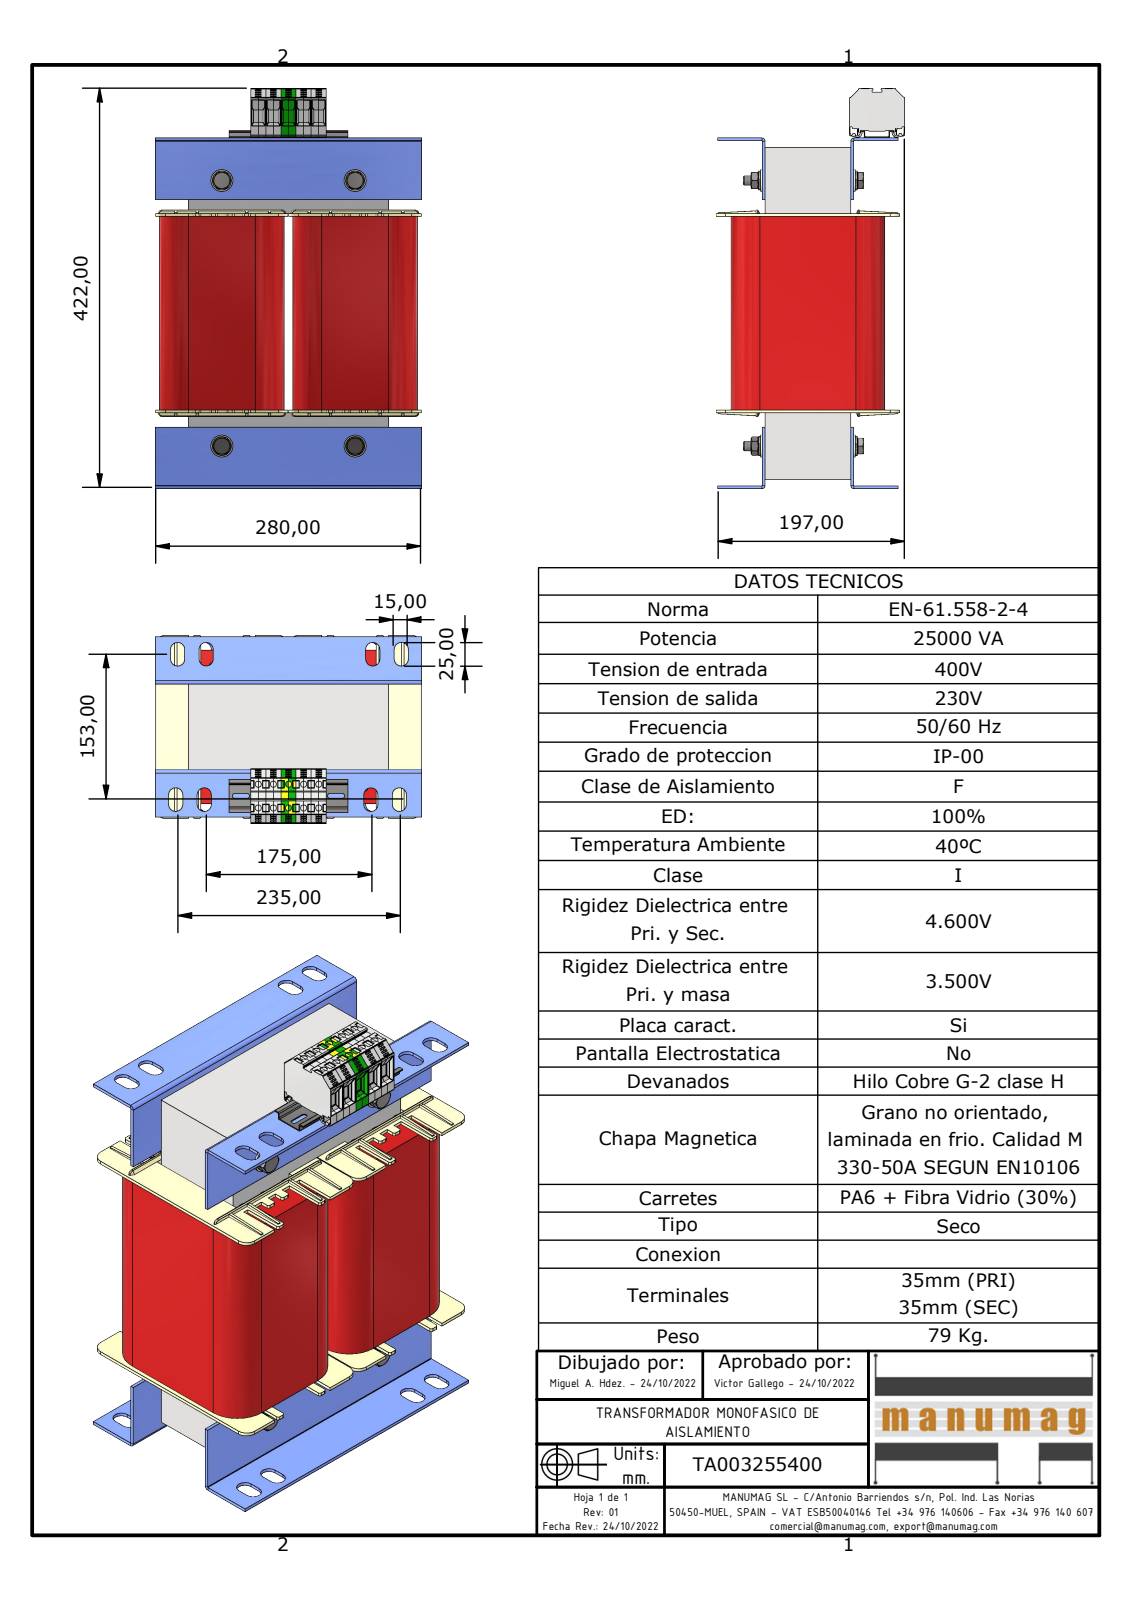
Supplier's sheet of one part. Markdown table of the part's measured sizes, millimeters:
| quantity | value |
| --- | --- |
| part name | TA003255400; UI350 x 210 - 90 (Rc70); RC 70 UI; centrador M10 (+7 more) |
| STEP written by | Autodesk Inventor 2023 (AUTOMOTIVE_DESIGN) |
| units | millimeters |
| bodies | 37 solids, 4798 faces (2768 planar, 1386 cylindrical, 644 other) |
| overall size | 422.3 × 280 × 198.3 |
| volume | 11 340 000 mm³ |
| surface area | 1 441 000 mm² |
| round holes (diameter × count) | 6.5 × 10, 2 × 4, 8.38 × 4, 10 × 4, 10.5 × 4, 14 × 4, 16 × 4 |
| round bosses / shafts (diameter × count) | 23 × 4, 20 × 4, 15.4 × 4, 11.5 × 4, 9.19 × 4 |
| partial cylindrical surfaces (radius × count) | 0.3 × 318, 0.5 × 136, 2 × 42, 1 × 32, 7.5 × 32, 0.25 × 18, 5 × 14, 2.6 × 10 |
| main face-to-face distances | 140, 70, 3, 2, 1.16, 3.16, 27.25, 28.41, 90, 30.41 |
| hole center spacings | 15.9, 29.63, 31.8, 40.45, 25, 47.7, 53.85, 7.95 |
